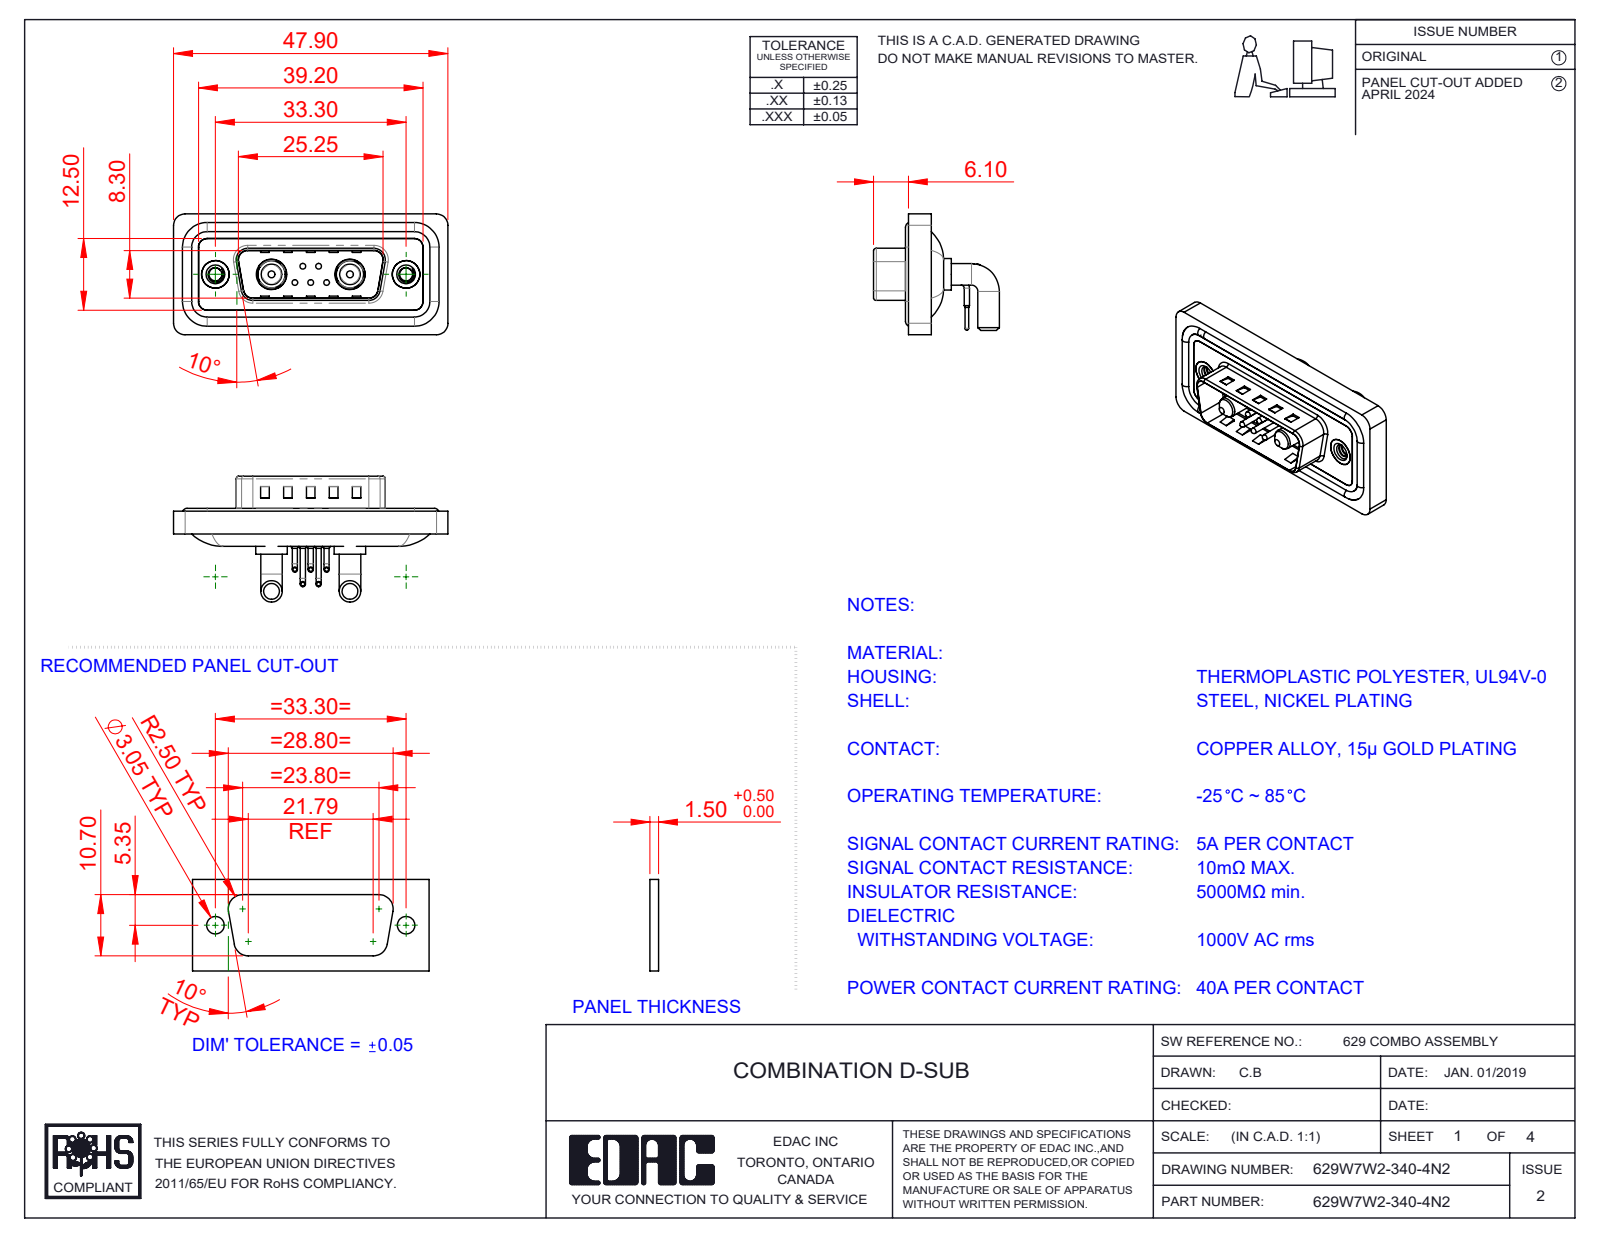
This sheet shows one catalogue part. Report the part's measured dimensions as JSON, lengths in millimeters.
{"part_name": "629Combo Contact Row 1; 629Combo Shell Rear_15 Contacts; 629W7W2-340-4N2; 629Combo Housing_7W2 (+5 more)", "step_written_by": "SolidWorks 2023 (CONFIG_CONTROL_DESIGN)", "units": "millimeters", "bodies": {"solids": 16, "faces": 1083, "planar": 517, "cylindrical": 406, "other": 160}, "overall_size": [47.9, 21.98, 21.1], "volume_mm3": 5837, "surface_area_mm2": 9229, "round_holes": [[0.75, 5], [1.6, 5], [2, 5], [2.26, 2], [4, 2], [4.8, 2], [4.85, 2], [5, 2], [5.3, 2]], "round_bosses_or_shafts": [[0.9, 10], [1.5, 5], [1, 5], [0.65, 5], [3.75, 4], [1.6, 4], [5.5, 2], [5.2, 2]], "partial_cylinders_radius": [[2, 20], [1.5, 18], [0.5, 8], [1.6, 8], [1.01, 5], [0.25, 4], [0.6, 4], [0.65, 4]], "face_to_face_distances": [0.4, 2.9, 0.8, 1.1, 2.1, 1.6, 2.5, 3.1, 4.5, 4.1], "hole_center_spacings": [3.16, 2.77, 9.8, 23.5, 4.31, 4.33, 5.03, 5.04]}
